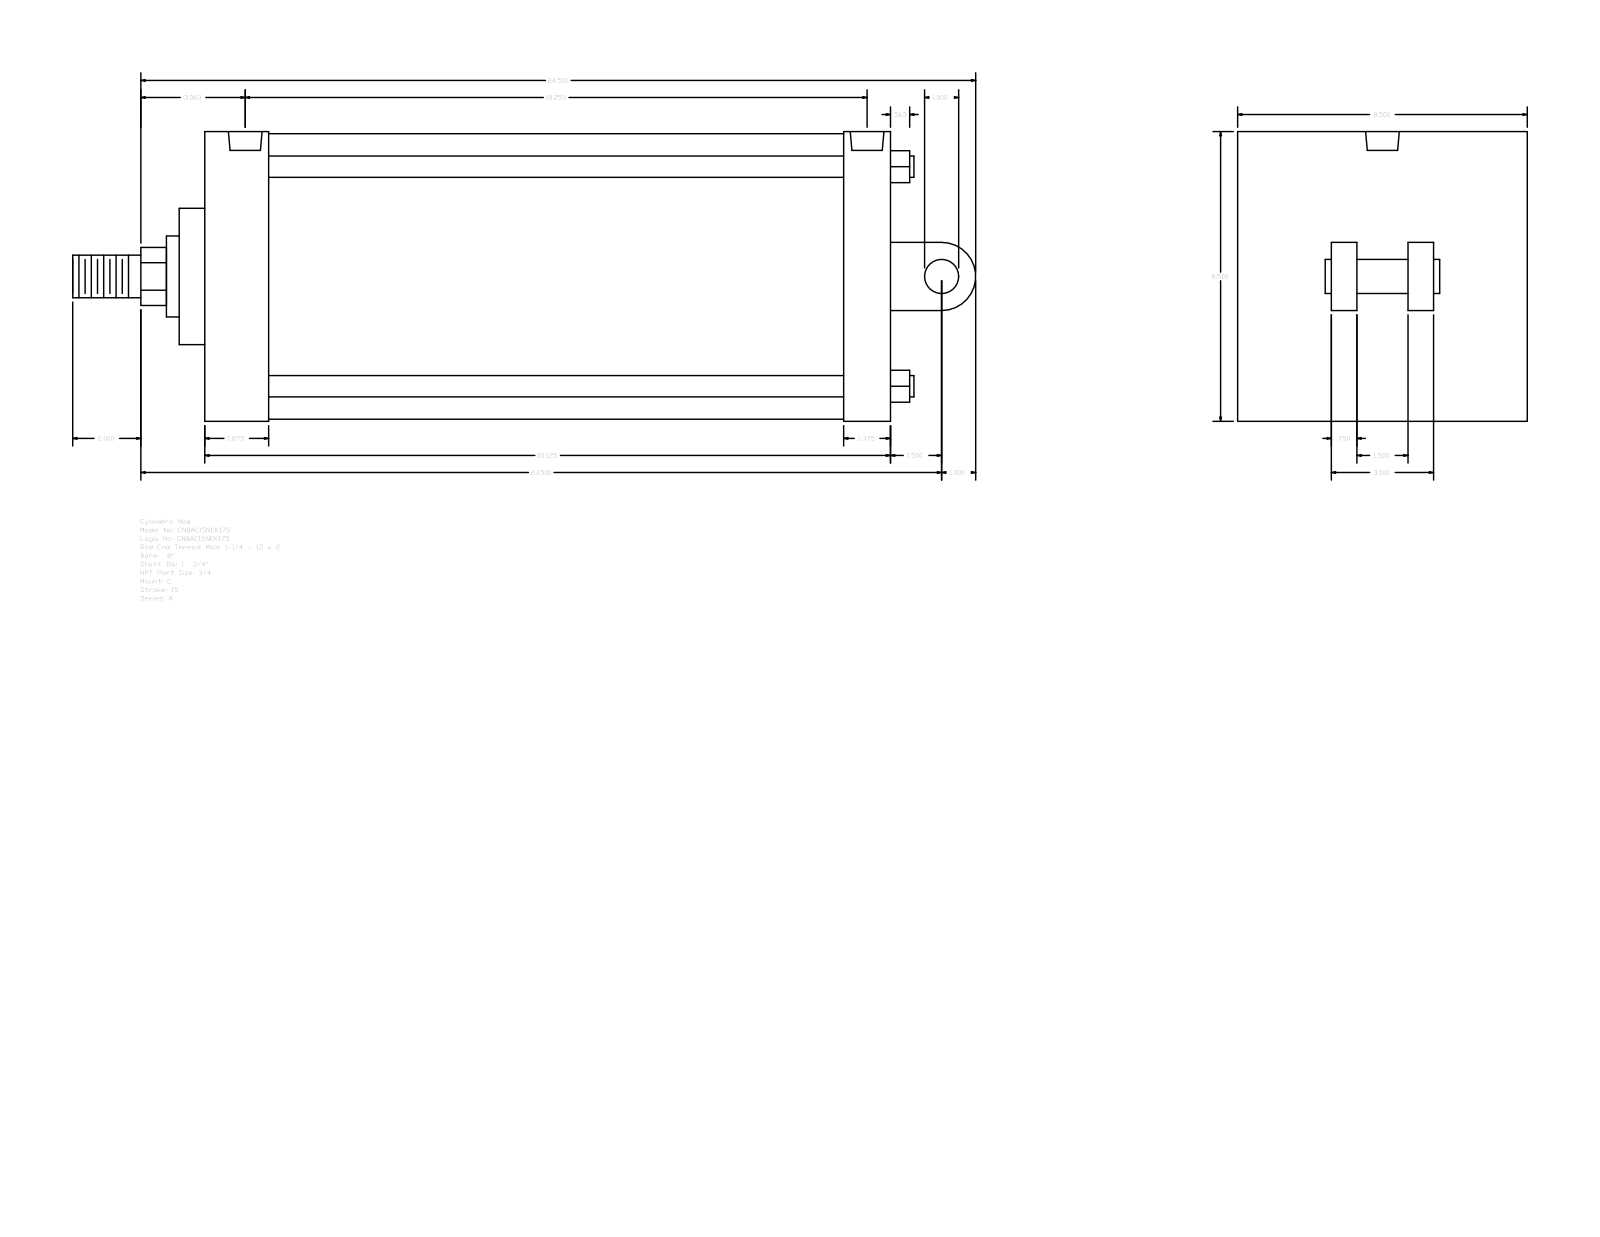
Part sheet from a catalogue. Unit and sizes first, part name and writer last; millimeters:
Units: millimetres
Overall size (bounding box): 673.1 × 215.9 × 215.9
Round holes (diameter × count): ⌀15.08 ×4, ⌀25.12 ×2
Round bosses / shafts (diameter × count): ⌀15.88 ×4, ⌀212.72 ×1, ⌀60.33 ×1, ⌀44.45 ×1, ⌀31.75 ×1, ⌀25.4 ×1
Partial cylindrical surfaces — rounded edges, fillets, slot ends (radius × count): R21.63 ×1, R25.4 ×1
Main face-to-face distances: 511.18, 215.9, 19.05, 57.15, 47.63, 463.55, 476.26, 428.63, 34.92, 69.85
Hole centre spacings: 6.35, 450.85, 457.2, 463.55
Bodies: 0 solids, 104 faces (75 planar, 29 cylindrical, 0 other)
Part name (STEP PRODUCT): A_C__0800_1.75
STEP written by: GSSL Pune (CONFIG_CONTROL_DESIGN)
